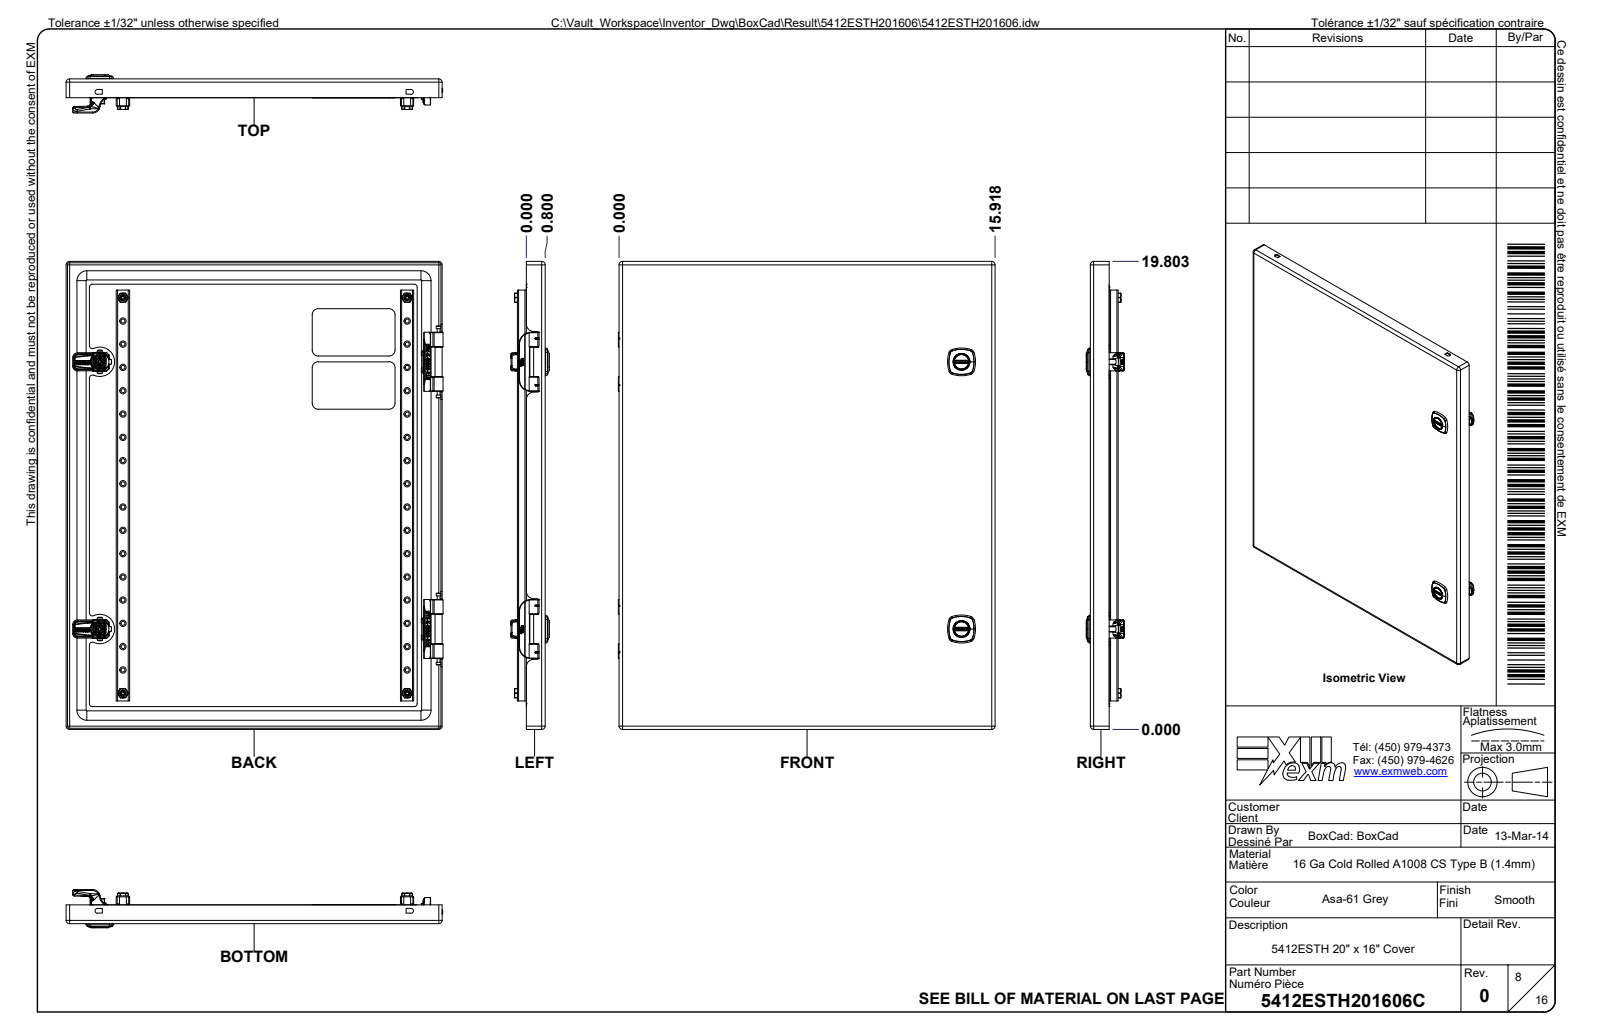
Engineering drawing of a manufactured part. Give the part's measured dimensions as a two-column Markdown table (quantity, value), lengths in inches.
| quantity | value |
| --- | --- |
| part name | 5412ESTH201606; 5412ESTH201606B; 5412ESTH201606B-P; STK-Q-16005 (+8 more) |
| STEP written by | Autodesk Inventor 2024 (AUTOMOTIVE_DESIGN) |
| units | inches |
| bodies | 87 solids, 14201 faces (4391 planar, 3865 cylindrical, 5945 other) |
| overall size | 22.25 × 16.003 × 7.603 |
| volume | 785.1 in³ |
| surface area | 5 468 in² |
| round holes (diameter × count) | 0.165 × 32, 0.03 × 10, 0.201 × 10, 0.5 × 10, 0.043 × 8, 0.311 × 6, 0.394 × 6, 0.406 × 6, 0.178 × 4, 0.268 × 4, 0.29 × 4, 0.335 × 4 |
| round bosses / shafts (diameter × count) | 0.237 × 32, 0.232 × 10, 0.03 × 10, 0.256 × 8, 0.039 × 8, 0.289 × 6, 0.177 × 6, 0.748 × 4 |
| partial cylindrical surfaces (radius × count) | 0.02 × 299, 0.008 × 182, 0.01 × 163, 0.039 × 69, 0.012 × 50, 0.125 × 48, 0.031 × 38, 0.059 × 37 |
| main face-to-face distances | 0.75, 0.053, 0.803, 6.278, 7.081, 7.028, 6.331, 7.135, 5.528, 15.144 |
| hole center spacings | 1.969, 0.984, 11.303, 2.953, 1.591, 3.937, 13.422, 17.411 |
